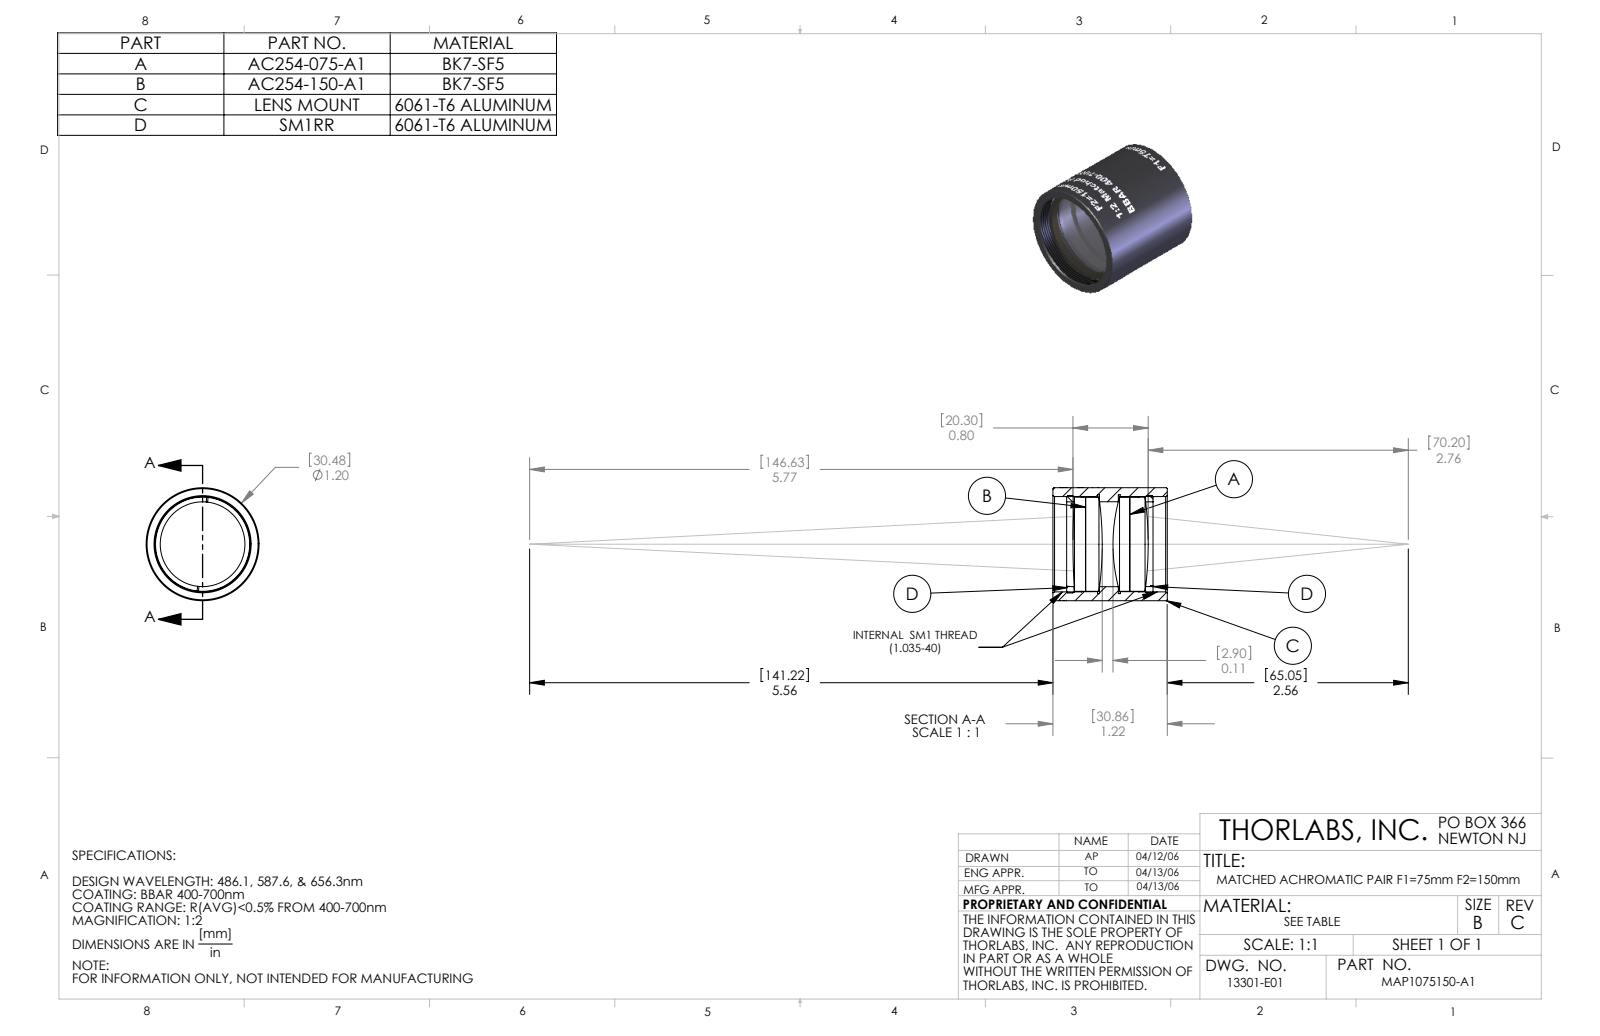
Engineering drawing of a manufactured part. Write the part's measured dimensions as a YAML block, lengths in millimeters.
part_name: "13301-E0W"
step_written_by: "SolidWorks 2007 (AUTOMOTIVE_DESIGN)"
units: millimeters
bodies: {solids: 0, faces: 141, planar: 18, cylindrical: 107, other: 16}
overall_size: [30.86, 30.48, 30.48]
round_holes:
  - {diameter: 22.86, count: 1}
  - {diameter: 25.7, count: 1}
round_bosses_or_shafts:
  - {diameter: 30.48, count: 1}
face_to_face_distances: [30.86, 3.85, 27.01, 27.16, 23.31, 3.7, 0.38, 4.48, 0.63, 22.68]
